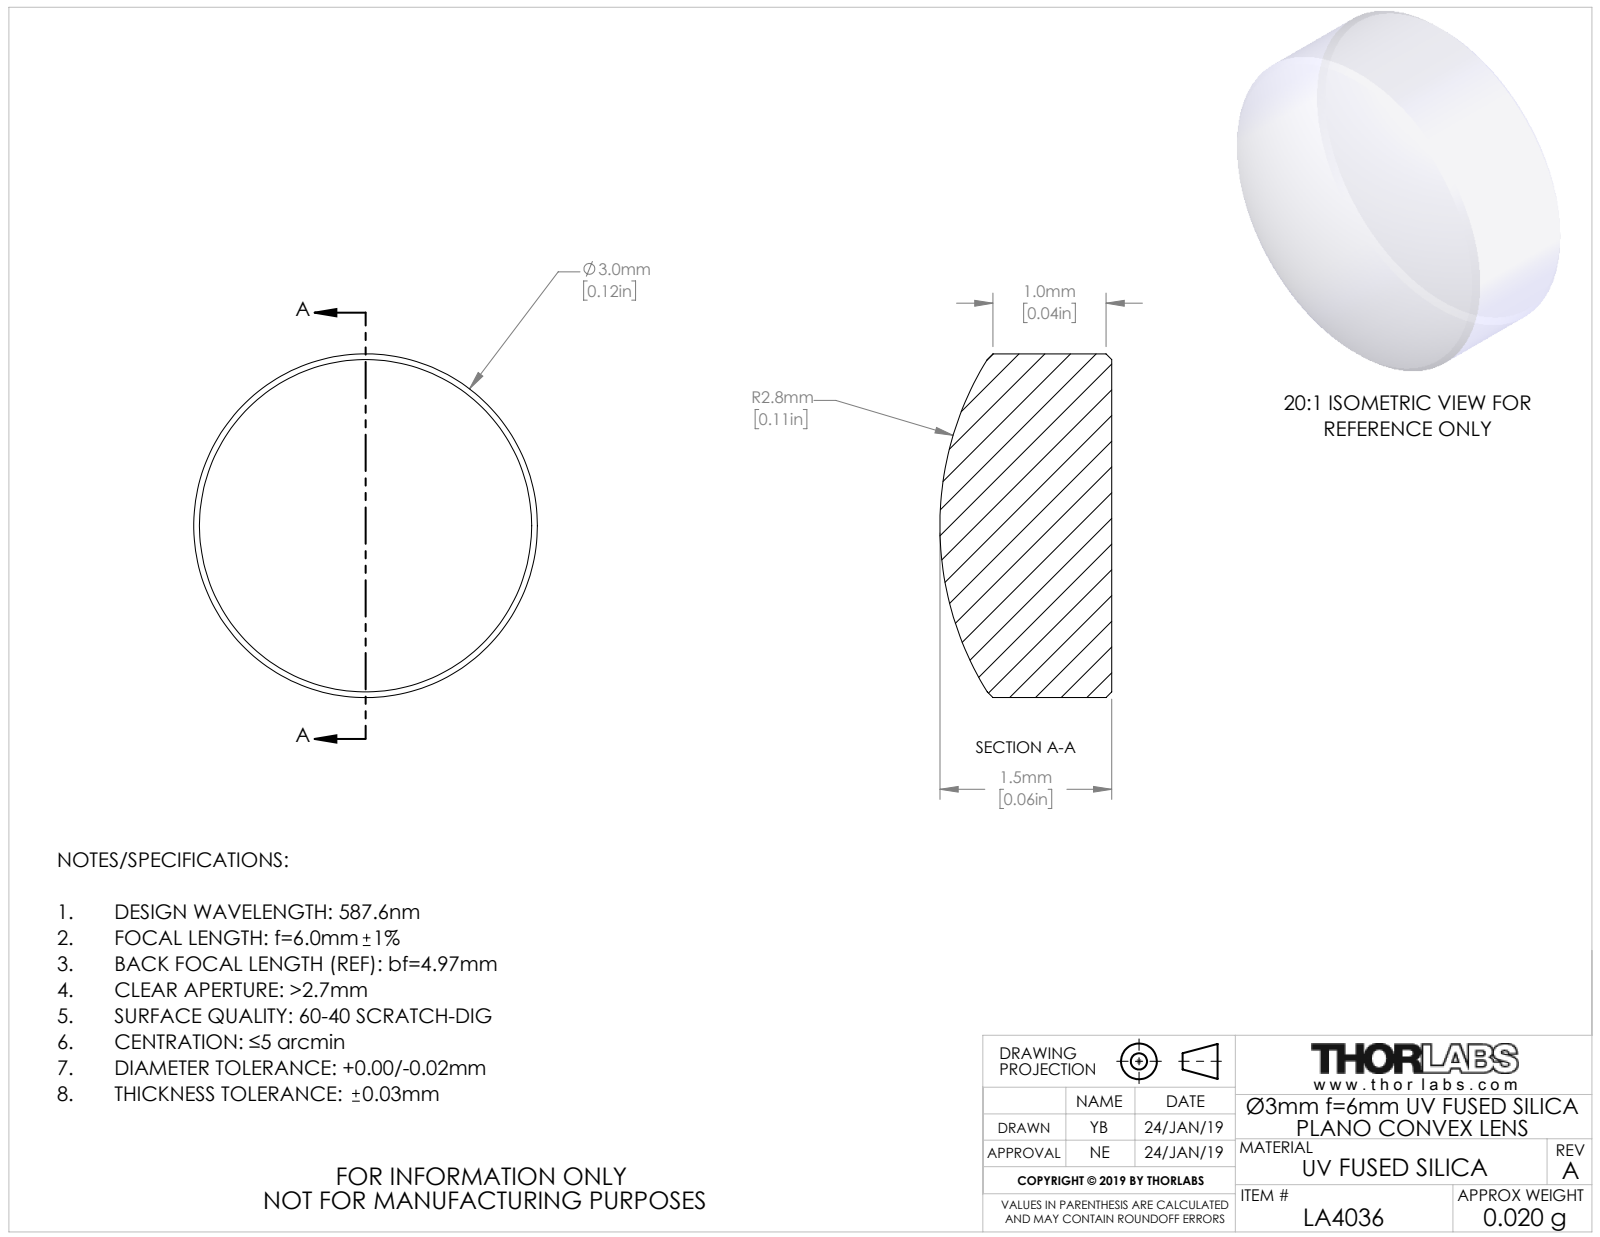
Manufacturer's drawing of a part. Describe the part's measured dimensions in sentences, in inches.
The part is named "TTN162796-E0W". Its 3-D file was written by "SolidWorks 2018 (CONFIG_CONTROL_DESIGN)". It is 1 solid with 9 faces: 1 planar, 2 cylindrical and 6 other. Overall it measures 0.118 by 0.118 by 0.059 inches. Its volume is 0.001 cubic inches and its surface area 0.037 square inches. Round bosses or shafts: 1 of diameter 0.118.
